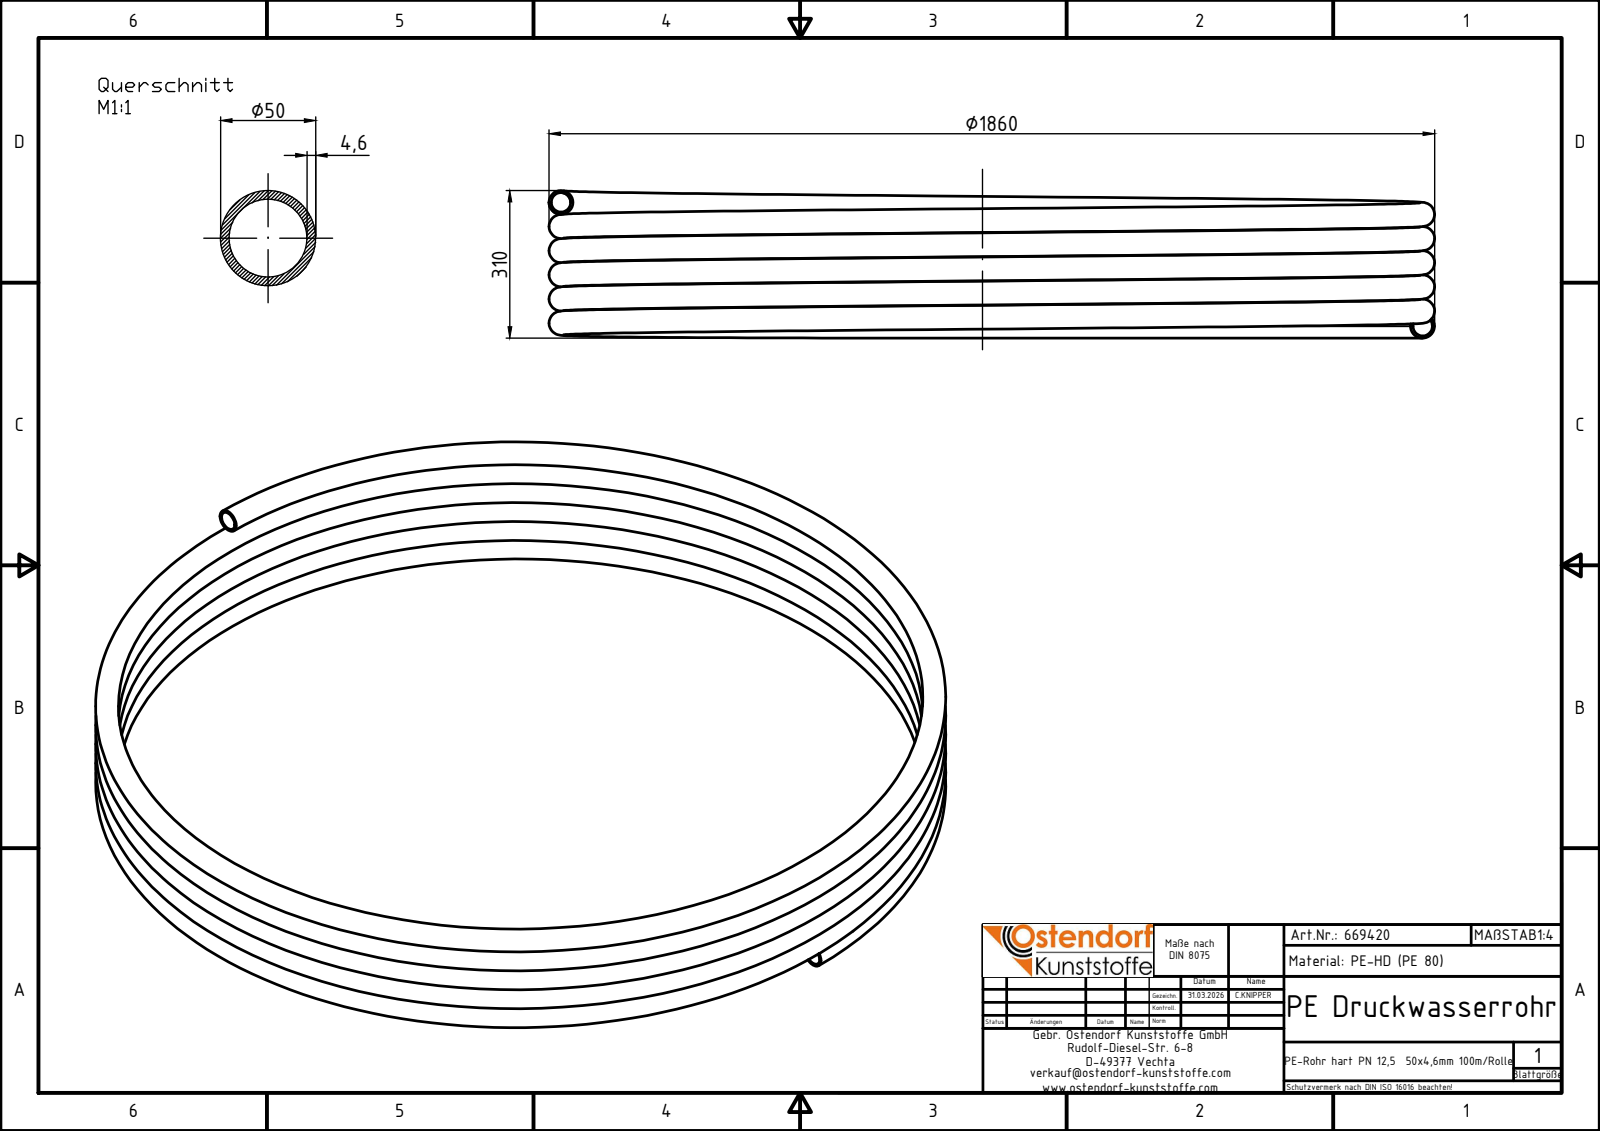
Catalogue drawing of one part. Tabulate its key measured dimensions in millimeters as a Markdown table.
| quantity | value |
| --- | --- |
| part name | 669420z |
| STEP written by | Autodesk Inventor 2024 (AUTOMOTIVE_DESIGN) |
| units | millimeters |
| bodies | 1 solid, 7 faces (3 planar, 0 cylindrical, 4 other) |
| overall size | 1860.01 × 1860.01 × 310.09 |
| volume | 20 090 000 mm³ |
| surface area | 8 763 000 mm² |
